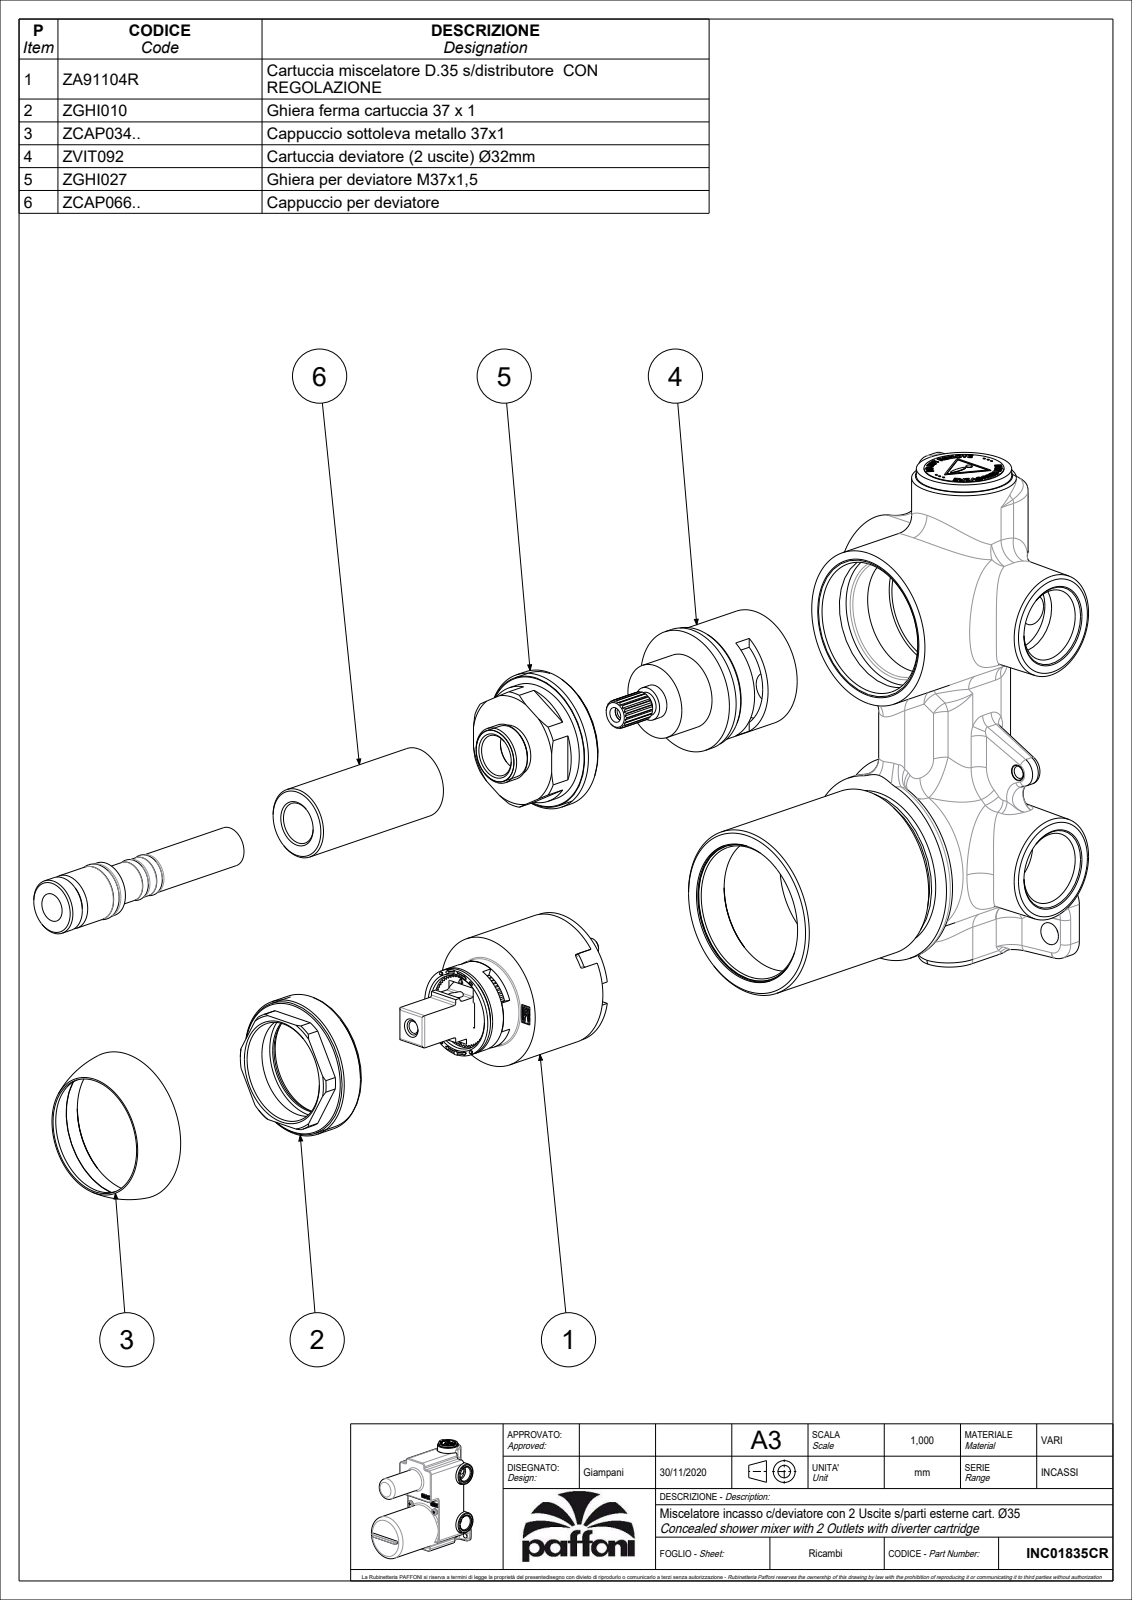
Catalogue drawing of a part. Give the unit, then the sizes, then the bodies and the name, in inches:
Units: inches
Overall size (bounding box): 5.423 × 5.394 × 2.598
Round holes (diameter × count): ⌀0.315 ×6, ⌀0.276 ×5, ⌀0.236 ×3, ⌀0.374 ×3, ⌀0.157 ×2, ⌀0.323 ×2, ⌀0.433 ×2, ⌀0.748 ×2, ⌀0.13 ×1, ⌀0.165 ×1, ⌀0.197 ×1, ⌀0.335 ×1
Round bosses / shafts (diameter × count): ⌀0.472 ×3, ⌀1.654 ×2, ⌀0.413 ×2, ⌀0.315 ×2, ⌀0.307 ×2, ⌀0.295 ×2, ⌀0.157 ×2, ⌀2.244 ×1
Partial cylindrical surfaces — rounded edges, fillets, slot ends (radius × count): R0.02 ×35, R0.039 ×34, R0.079 ×25, R0.157 ×18, R0.197 ×16, R0.006 ×11, R0.008 ×9, R0.059 ×8
Main face-to-face distances: 0.079, 2.205, 2.283, 2.165, 2.126, 0.315, 0.492, 0.65, 0.157, 2.244
Hole centre spacings: 0.291, 0.339, 0.391, 0.564, 2.25, 2.445, 2.544, 2.677
Volume: 19.33 in³ · Surface area: 257.8 in²
Bodies: 2 solids, 2323 faces (1039 planar, 482 cylindrical, 802 other)
Part name (STEP PRODUCT): INC01835CR
STEP written by: CREO PARAMETRIC BY PTC INC, 2020044 (CONFIG_CONTROL_DESIGN)
